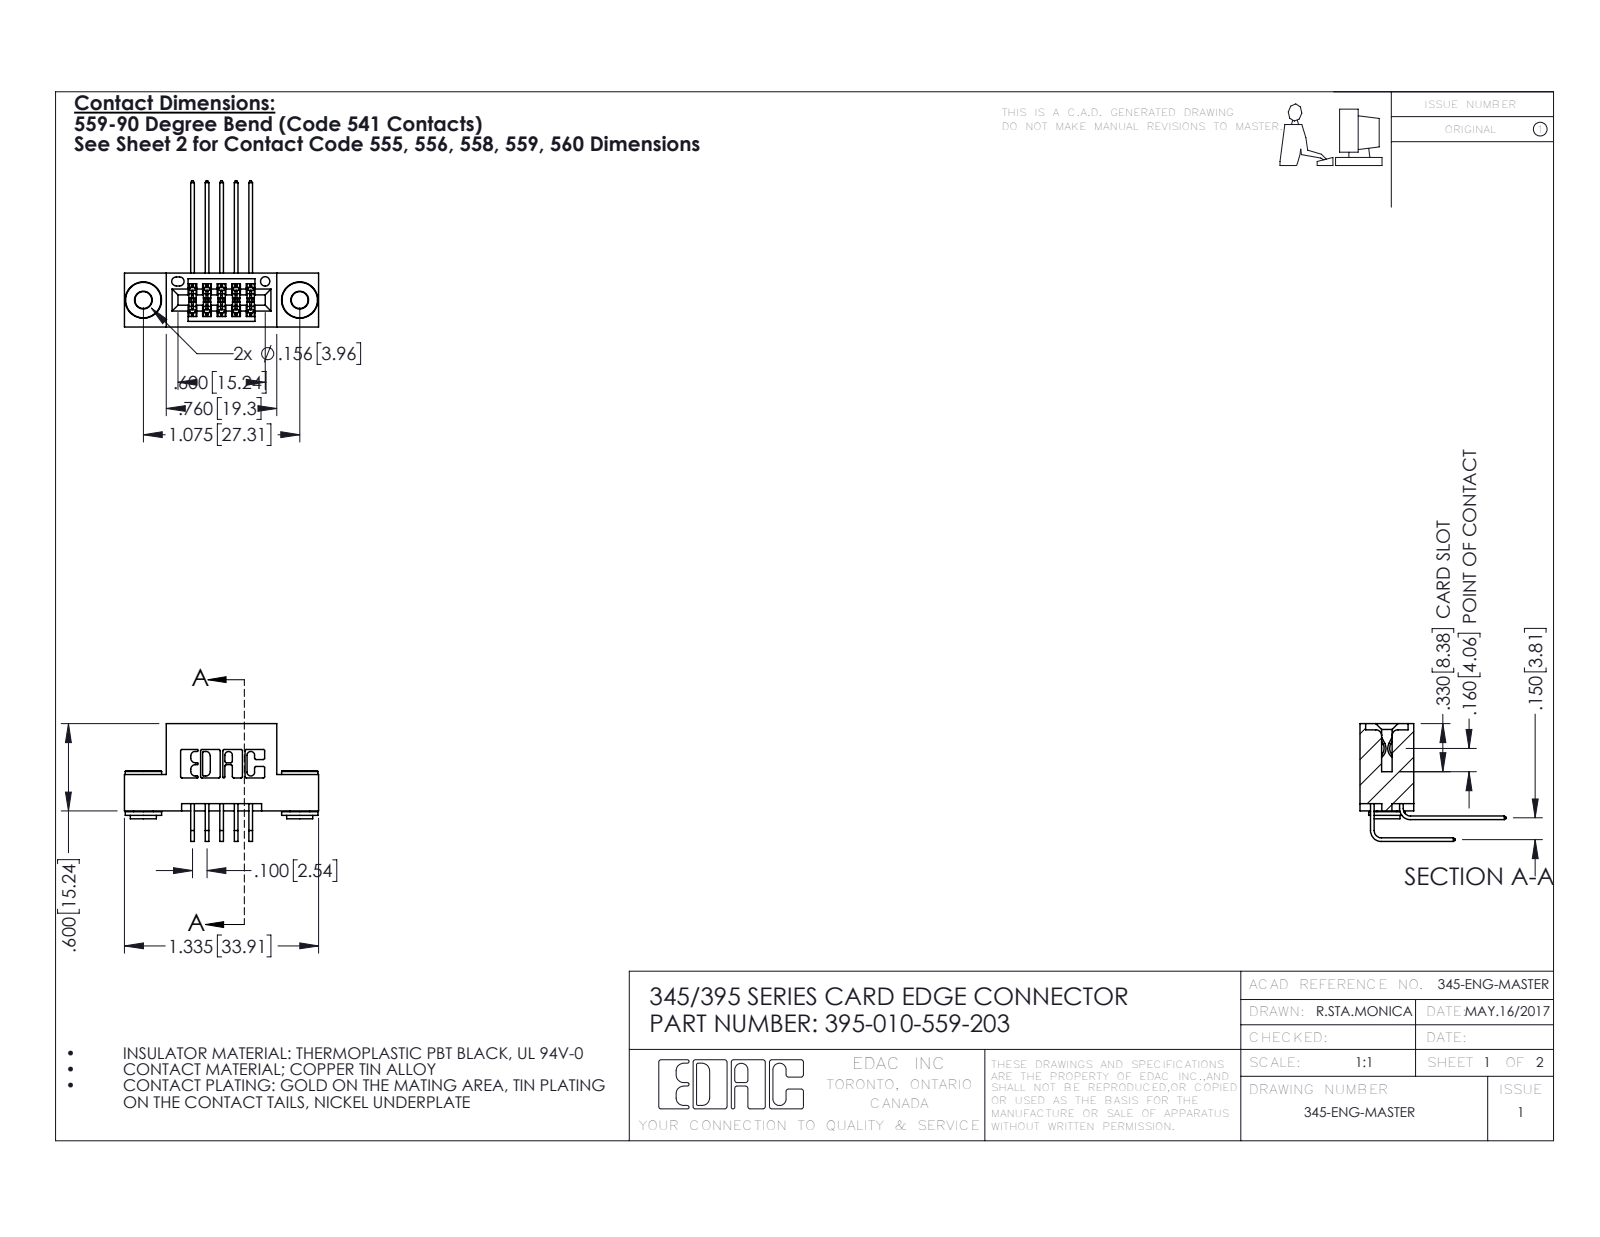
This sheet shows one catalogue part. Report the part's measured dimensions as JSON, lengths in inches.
{"part_name": "345 Part_Flush Mounting Lugs - 0.156 Dia-TH; 345-250-002_345-250-002-102; 345-292-001_558 559 Tail - 1; 395-010-559-203 (+1 more)", "step_written_by": "SolidWorks 2016 (CONFIG_CONTROL_DESIGN)", "units": "inches", "bodies": {"solids": 13, "faces": 684, "planar": 440, "cylindrical": 236, "other": 8}, "overall_size": [1.335, 1.005, 0.809], "volume_in3": 0.185, "surface_area_in2": 6.564, "round_holes": [[0.116, 2], [0.156, 2], [0.064, 1]], "round_bosses_or_shafts": [[0.25, 2], [0.18, 2], [0.136, 2]], "partial_cylinders_radius": [[0.01, 22], [0.006, 16], [0.007, 6], [0.031, 6], [0.026, 3], [0.014, 2], [0.019, 2], [0.022, 2]], "face_to_face_distances": [0.2, 0.1, 0.37, 0.072, 0.298, 0.025, 0.25, 0.3, 0.225, 0.15], "hole_center_spacings": [0.27, 0.847, 1.075]}
